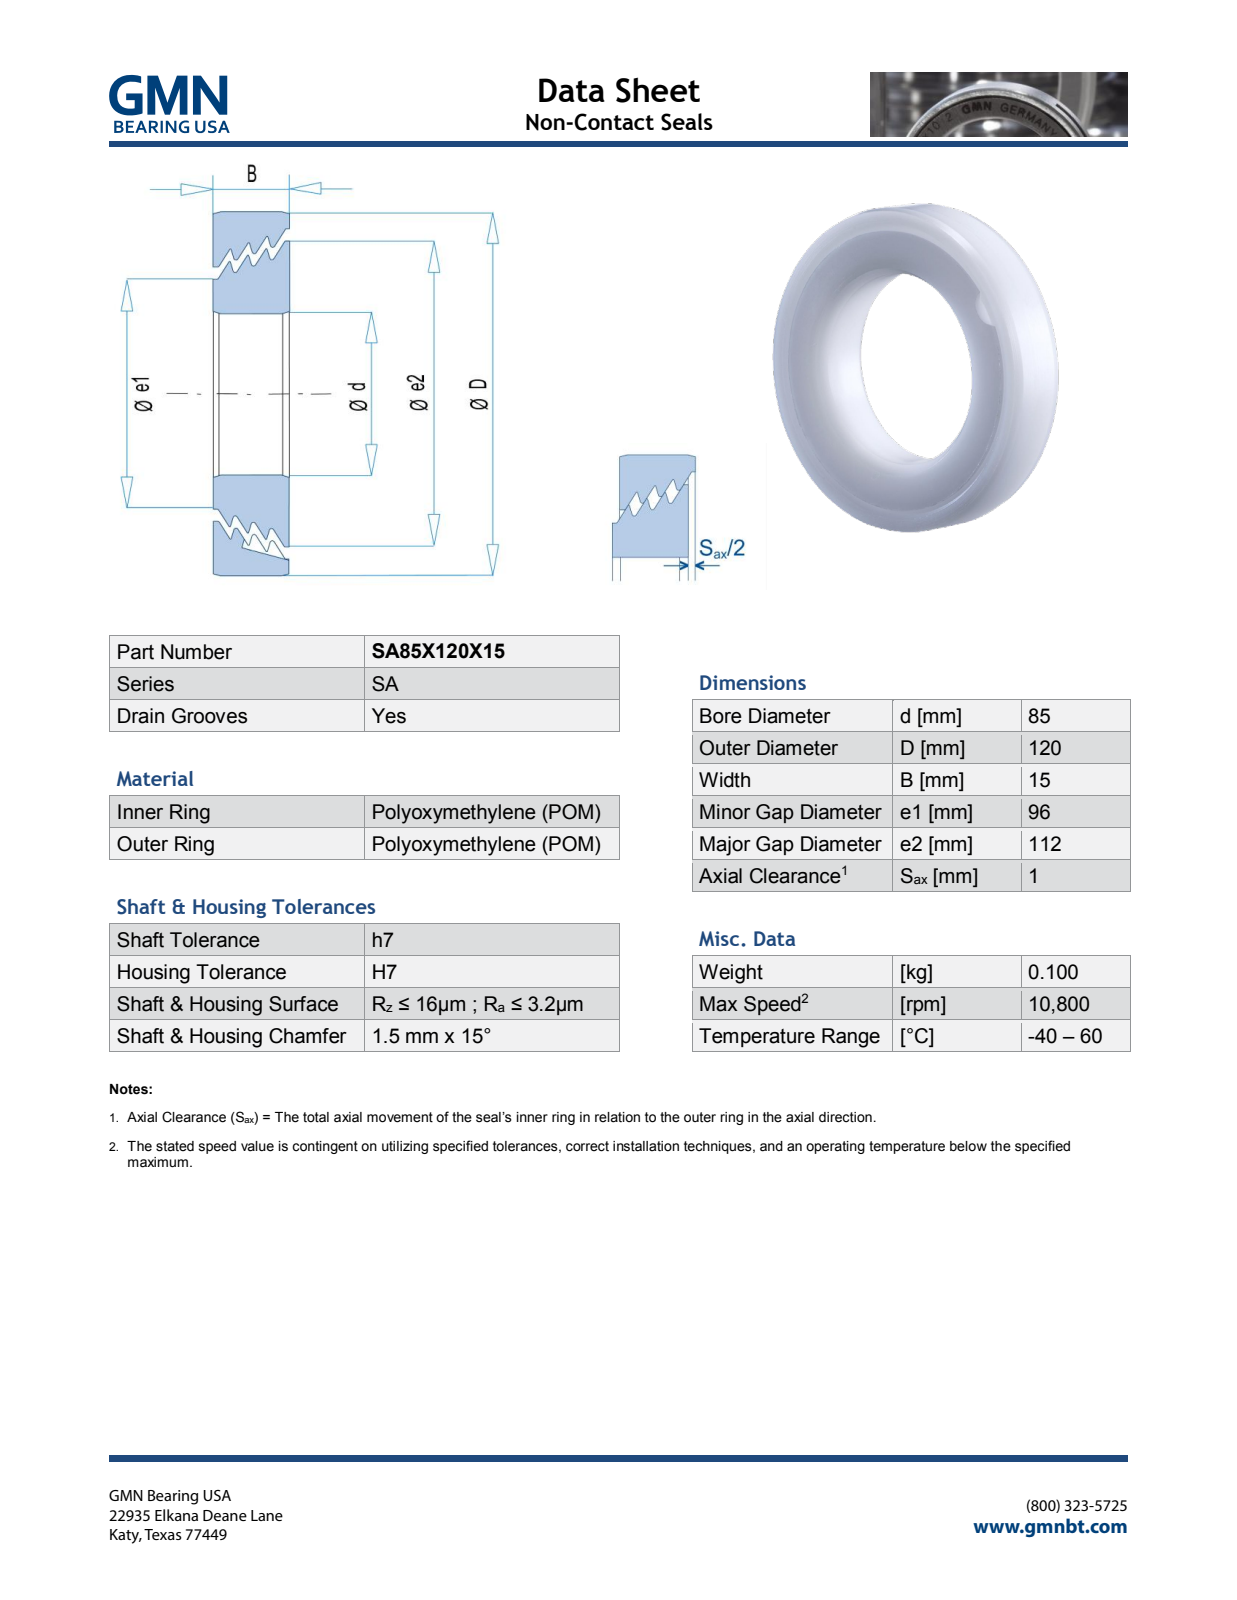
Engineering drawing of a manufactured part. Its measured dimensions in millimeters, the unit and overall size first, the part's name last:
Units: millimetres
Overall size (bounding box): 120 × 120 × 15.07
Round holes (diameter × count): ⌀85 ×1, ⌀97.63 ×1, ⌀113.63 ×1
Round bosses / shafts (diameter × count): ⌀120 ×1, ⌀112 ×1, ⌀96 ×1
Partial cylindrical surfaces — rounded edges, fillets, slot ends (radius × count): R6 ×1
Main face-to-face distances: 15, 15.07, 9.26, 9.19, 5.81, 0.36, 0.37, 2.53, 2.89, 0.31
Volume: 78 926 mm³ · Surface area: 37 790 mm²
Bodies: 2 solids, 700 faces (615 planar, 13 cylindrical, 72 other)
Part name (STEP PRODUCT): SA85X120X15_PRT
STEP written by: PRO/ENGINEER BY PARAMETRIC TECHNOLOGY CORPORATION, 2013150 (AUTOMOTIVE_DESIGN)
